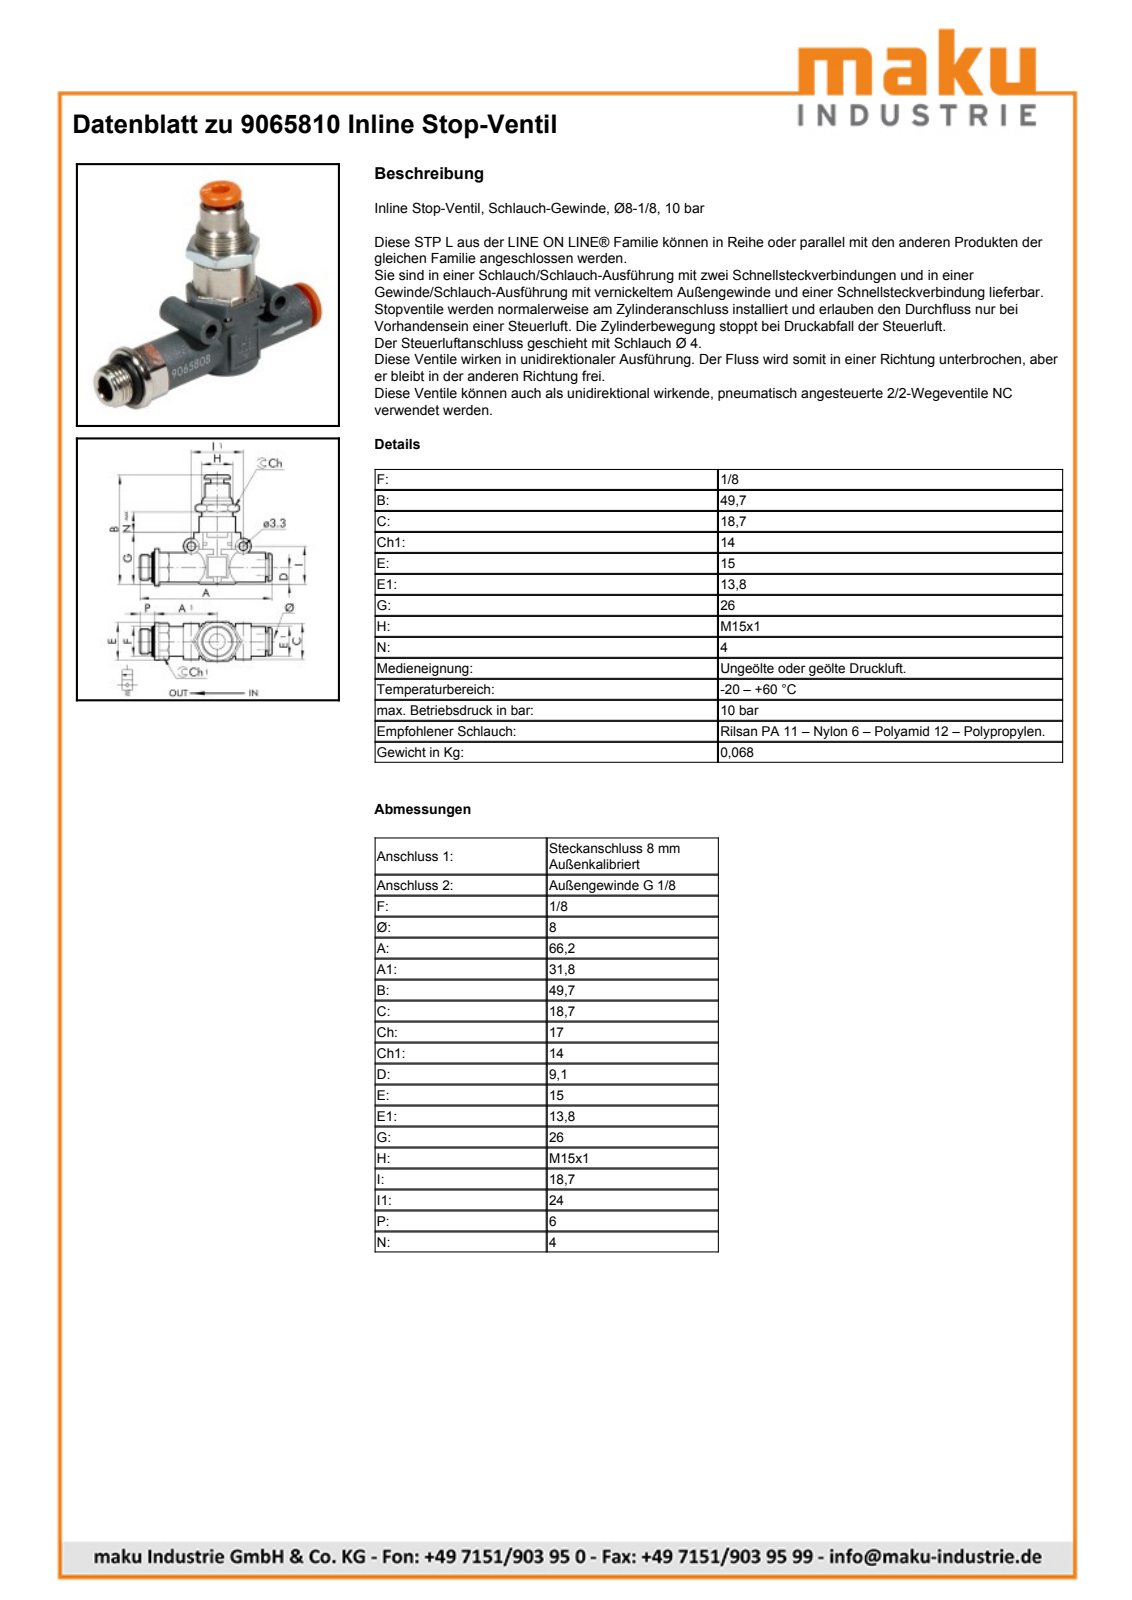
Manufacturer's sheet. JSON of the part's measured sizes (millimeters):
{"part_name": "9065810; LINE-ON-LINE D8 PNV_L-body; LINE-ON-LINE D8 VNR-L bushing; LINE-ON-LINE D8-1/8 RML-thread port (+2 more)", "step_written_by": "PARTsolutions (AUTOMOTIVE_DESIGN)", "units": "millimeters", "bodies": {"solids": 5, "faces": 197, "planar": 122, "cylindrical": 59, "other": 16}, "overall_size": [66.2, 49.7, 18.7], "volume_mm3": 12627, "surface_area_mm2": 11041, "round_holes": [[3.3, 2], [6, 2], [3.5, 1], [5, 1], [5.53, 1], [6.2, 1], [8.1, 1], [11, 1], [11.65, 1], [12.5, 1], [15, 1]], "round_bosses_or_shafts": [[7.2, 2], [6, 2], [18.8, 1], [18, 1], [15, 1], [13.8, 1], [13.6, 1], [12.8, 1]], "partial_cylinders_radius": [[3.75, 1], [7.95, 1], [10.35, 1], [11.45, 1]], "face_to_face_distances": [24.1, 43, 4.1, 20, 18.5, 20.5, 47.1, 23, 22, 14], "hole_center_spacings": [15.37, 24]}
